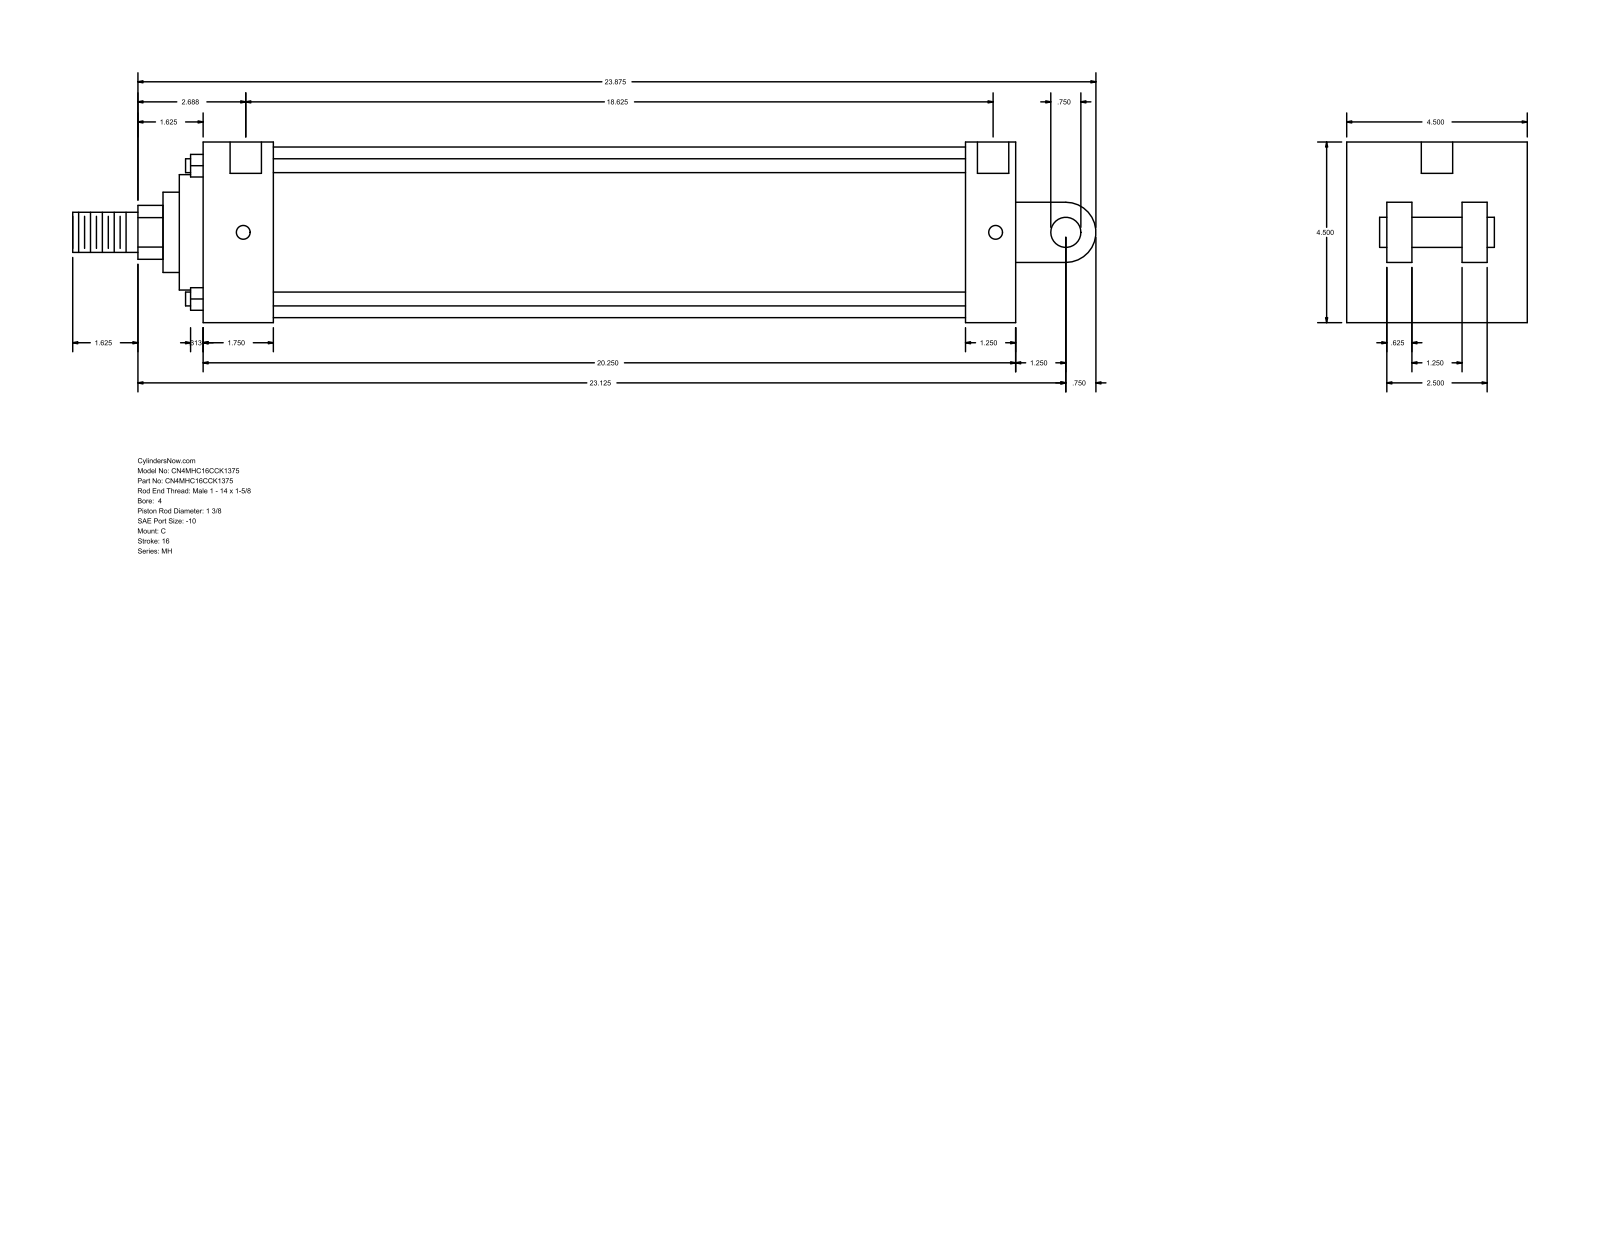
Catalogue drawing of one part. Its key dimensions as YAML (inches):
part_name: "MH_C__0400_1.375"
step_written_by: "GSSL Pune (CONFIG_CONTROL_DESIGN)"
units: inches
bodies: {solids: 0, faces: 101, planar: 71, cylindrical: 30, other: 0}
overall_size: [25.5, 4.5, 4.5]
round_holes:
  - {diameter: 0.344, count: 4}
  - {diameter: 0.781, count: 2}
round_bosses_or_shafts:
  - {diameter: 0.345, count: 4}
  - {diameter: 4.25, count: 1}
  - {diameter: 2.875, count: 1}
  - {diameter: 2, count: 1}
  - {diameter: 1.375, count: 1}
  - {diameter: 1, count: 1}
  - {diameter: 0.75, count: 1}
partial_cylinders:
  - {radius: 0.672, count: 1}
  - {radius: 0.75, count: 1}
face_to_face_distances: [4.5, 20.25, 1.75, 19, 17.25, 18.5, 1.25, 1.625, 2.875, 1.5]
hole_center_spacings: [18.75, 0.062, 0.063, 18.625, 18.687, 18.688]
